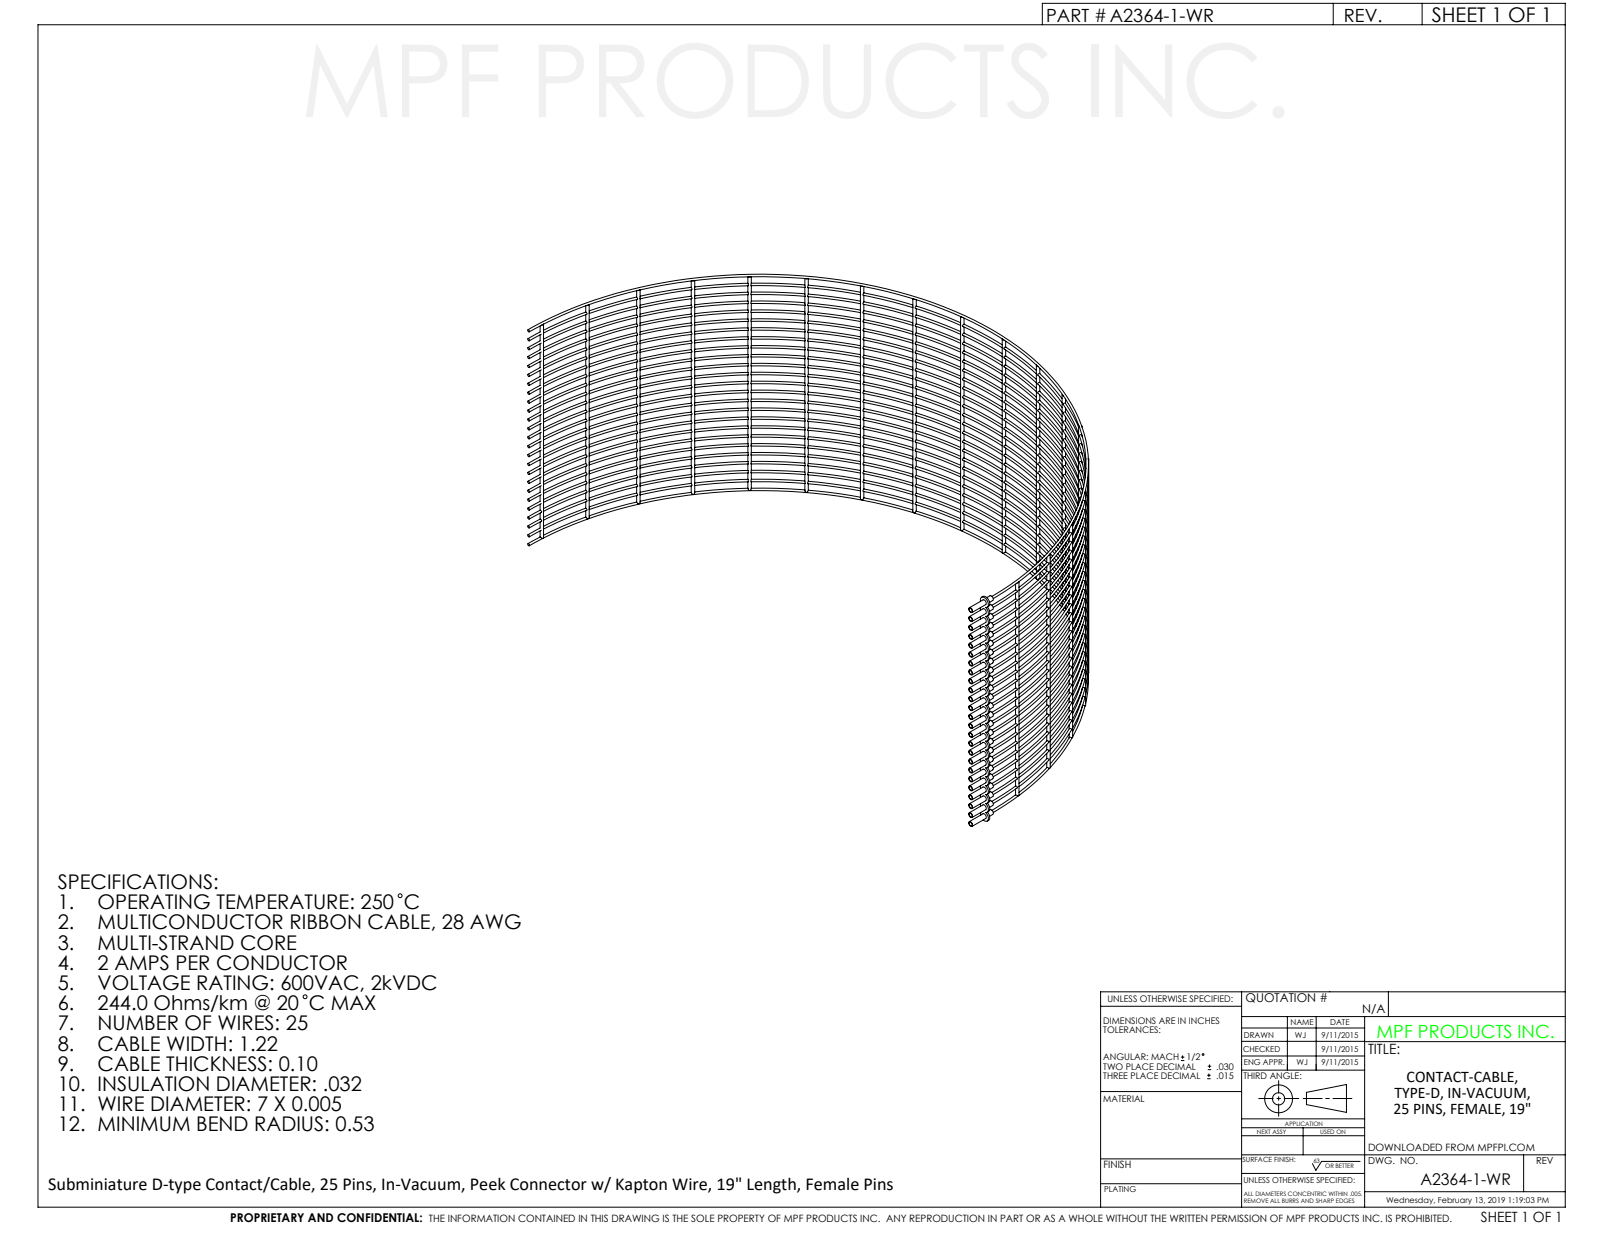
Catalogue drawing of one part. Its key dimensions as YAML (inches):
part_name: "A2364-1-WR"
step_written_by: "SolidWorks 2012 (CONFIG_CONTROL_DESIGN)"
units: inches
bodies: {solids: 1, faces: 1381, planar: 175, cylindrical: 260, other: 946}
overall_size: [6.064, 3.28, 2.505]
volume: 0.14
surface_area: 21.95
round_holes:
  - {diameter: 0.038, count: 25}
round_bosses_or_shafts:
  - {diameter: 0.05, count: 25}
  - {diameter: 0.105, count: 24}
  - {diameter: 0.032, count: 18}
partial_cylinders:
  - {radius: 0.053, count: 1}
face_to_face_distances: [0.018, 0.074, 0.091, 0.159, 0.086, 0.068, 0.269, 0.195, 0.177, 0.109]
hole_center_spacings: [0.1, 0.2, 0.3, 0.4, 0.5, 0.6, 0.7, 0.8]
